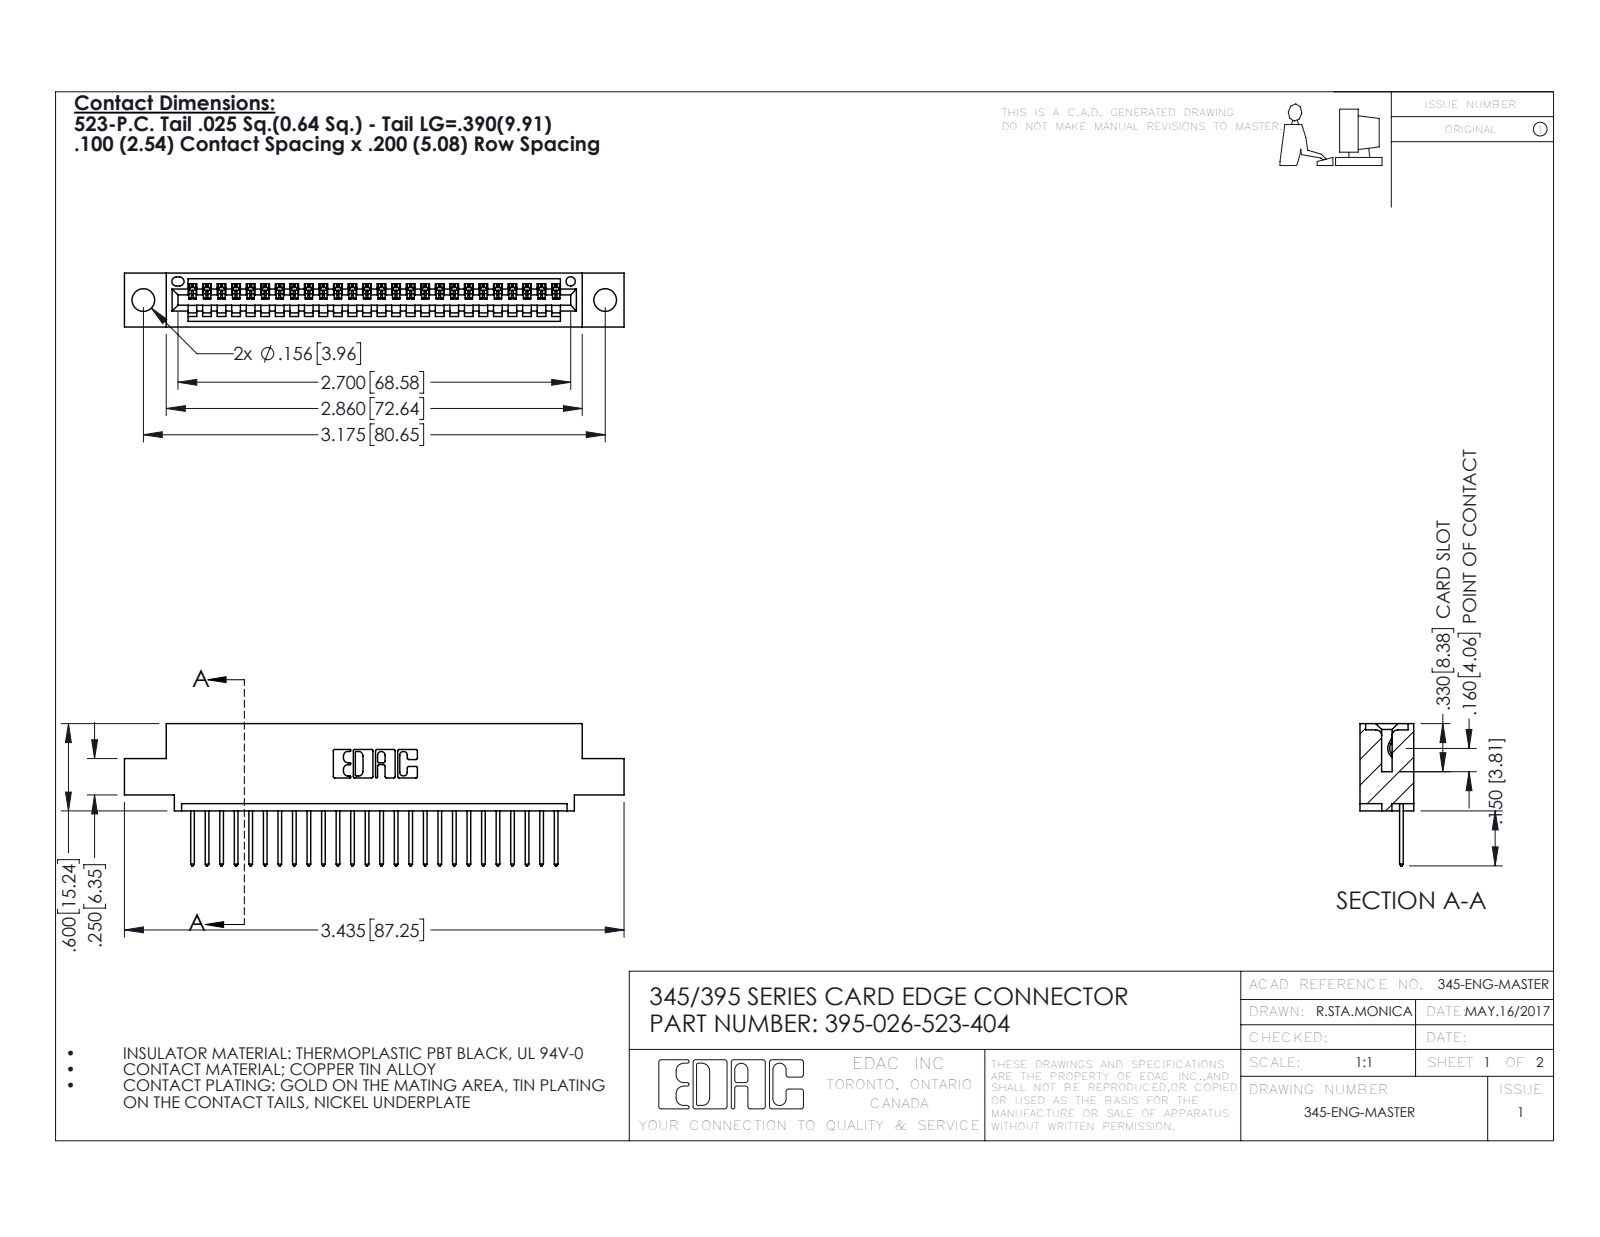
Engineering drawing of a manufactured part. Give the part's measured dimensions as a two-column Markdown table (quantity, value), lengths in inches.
| quantity | value |
| --- | --- |
| part name | 395-026-523-404; 345-292-001_345-293-123; 345 Part_0.110 Offset - 0.156 Dia-TH |
| STEP written by | SolidWorks 2016 (CONFIG_CONTROL_DESIGN) |
| units | inches |
| bodies | 27 solids, 1638 faces (1124 planar, 514 cylindrical, 0 other) |
| overall size | 3.435 × 0.977 × 0.37 |
| volume | 0.487 in³ |
| surface area | 15.98 in² |
| round holes (diameter × count) | 0.156 × 2, 0.064 × 1 |
| partial cylindrical surfaces (radius × count) | 0.006 × 52, 0.01 × 52, 0.01 × 22, 0.007 × 6, 0.031 × 6, 0.026 × 3, 0.031 × 2, 0.04 × 2 |
| main face-to-face distances | 0.298, 0.072, 0.37, 0.2, 0.098, 0.272, 0.025, 0.225, 0.149, 0.072 |
| hole center spacings | 0.27, 2.94, 3.175 |
